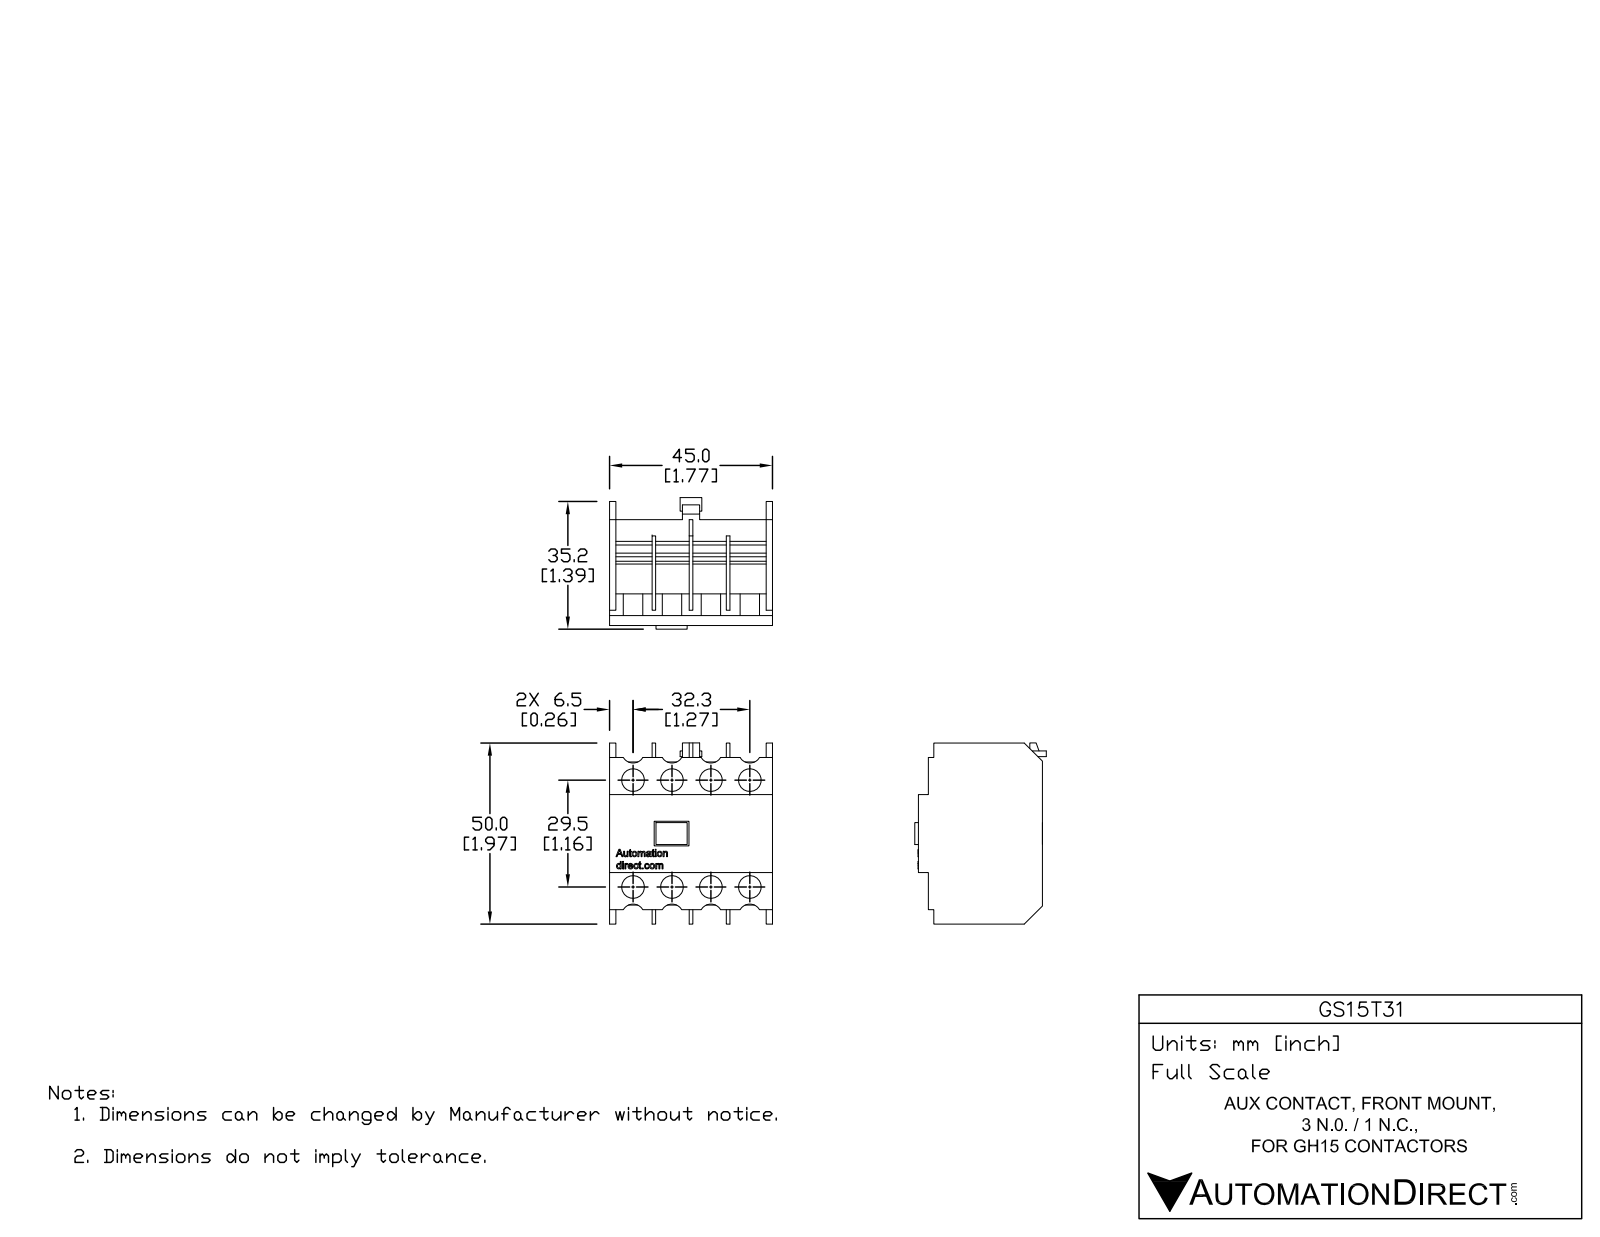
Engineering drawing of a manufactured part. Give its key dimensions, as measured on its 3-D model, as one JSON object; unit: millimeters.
{"part_name": "GH15T31", "step_written_by": "SolidWorks 2009 (CONFIG_CONTROL_DESIGN)", "units": "millimeters", "bodies": {"solids": 1, "faces": 509, "planar": 359, "cylindrical": 24, "other": 126}, "overall_size": [50.03, 45, 36.32], "volume_mm3": 38863, "surface_area_mm2": 16844, "round_holes": [[6.25, 8]], "partial_cylinders_radius": [[3.12, 8]], "face_to_face_distances": [10.25, 20.5, 45, 1.75, 43.25, 1, 6, 22, 14.25, 12.75], "hole_center_spacings": [10.75, 31.4, 21.5, 29.5, 36.5, 32.25, 43.71]}
